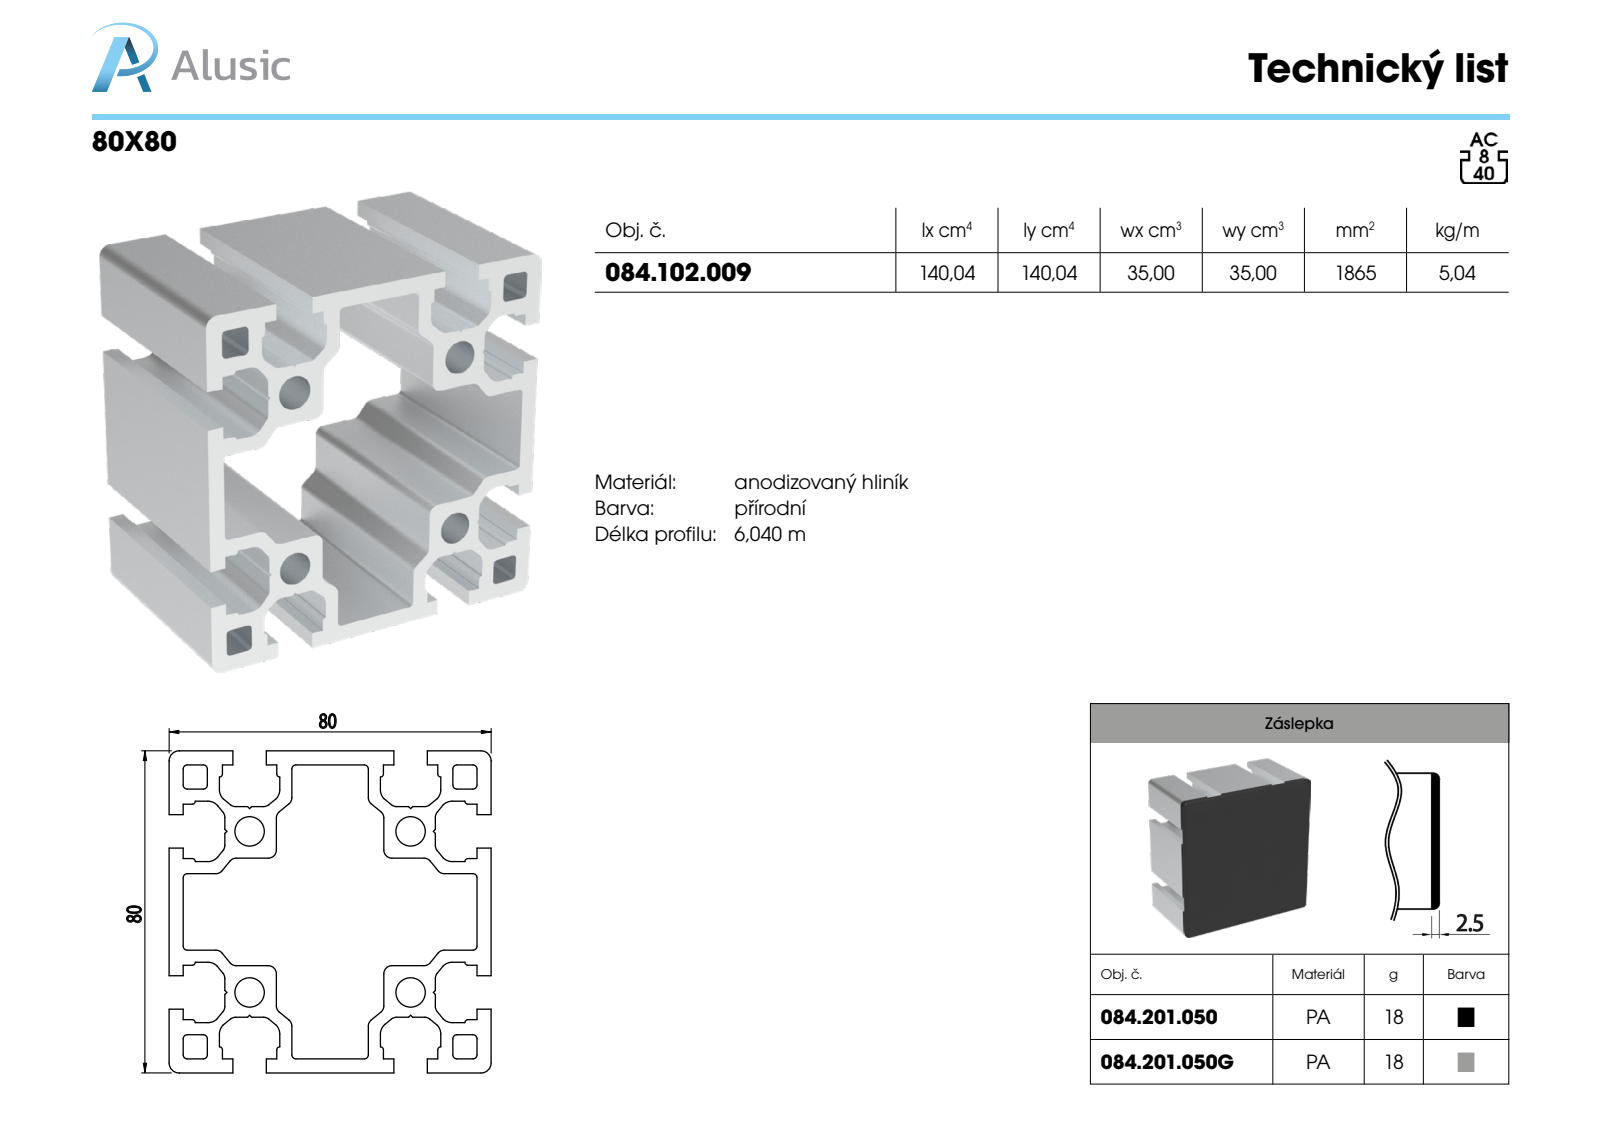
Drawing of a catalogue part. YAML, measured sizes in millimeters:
part_name: "084.102.009"
step_written_by: "SolidWorks 2011 (CONFIG_CONTROL_DESIGN)"
units: millimeters
bodies: {solids: 1, faces: 274, planar: 170, cylindrical: 104, other: 0}
overall_size: [100, 80, 80]
volume: 186215
surface_area: 109585
round_holes:
  - {diameter: 7.3, count: 4}
partial_cylinders:
  - {radius: 2, count: 36}
  - {radius: 1, count: 24}
  - {radius: 0.75, count: 16}
  - {radius: 3.2, count: 16}
  - {radius: 2.5, count: 4}
face_to_face_distances: [3.5, 76.5, 80, 40, 73, 3, 26.65, 53.35, 23.15, 49.85]
hole_center_spacings: [40, 56.57]
